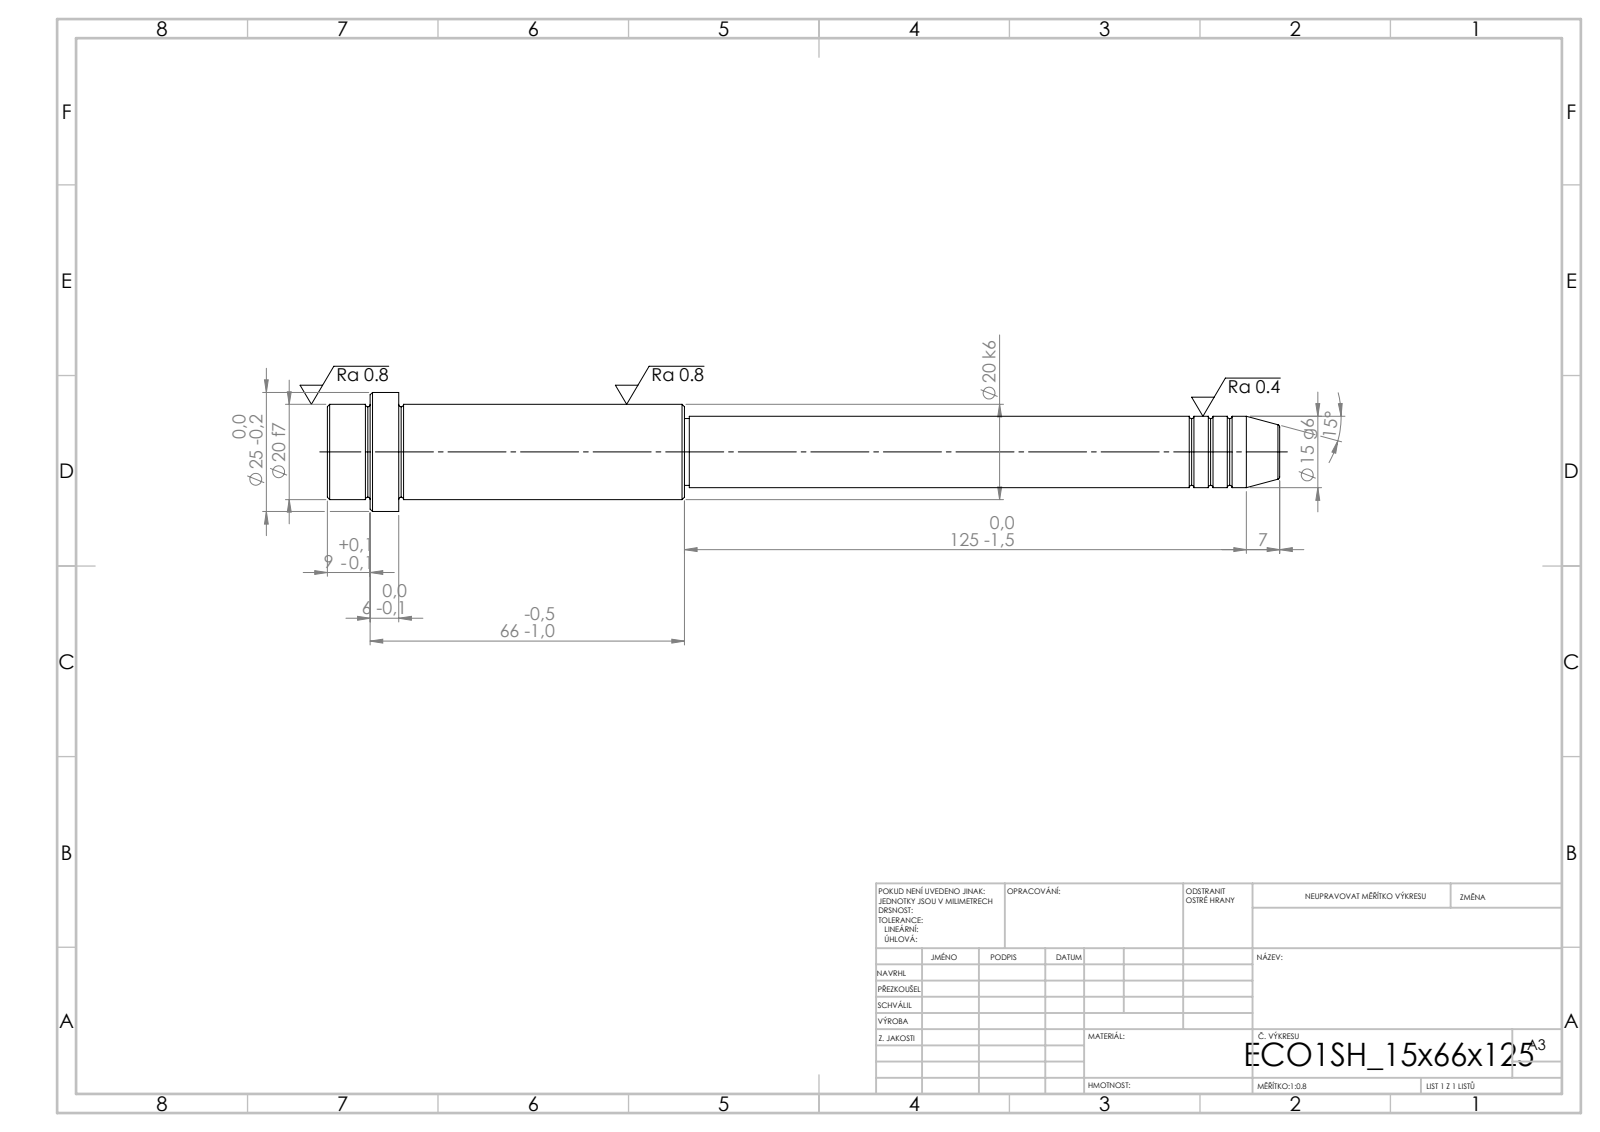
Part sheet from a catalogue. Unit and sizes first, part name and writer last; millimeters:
Units: millimetres
Overall size (bounding box): 200 × 25 × 25
Round bosses / shafts (diameter × count): ⌀25 ×1, ⌀20 ×1, ⌀15 ×1, ⌀14 ×1
Main face-to-face distances: 15, 6, 9, 60, 66, 75, 125, 185, 191, 200
Volume: 46 277 mm³ · Surface area: 11 685 mm²
Bodies: 1 solid, 52 faces (6 planar, 16 cylindrical, 30 other)
STEP written by: SolidWorks 2019 (CONFIG_CONTROL_DESIGN)
